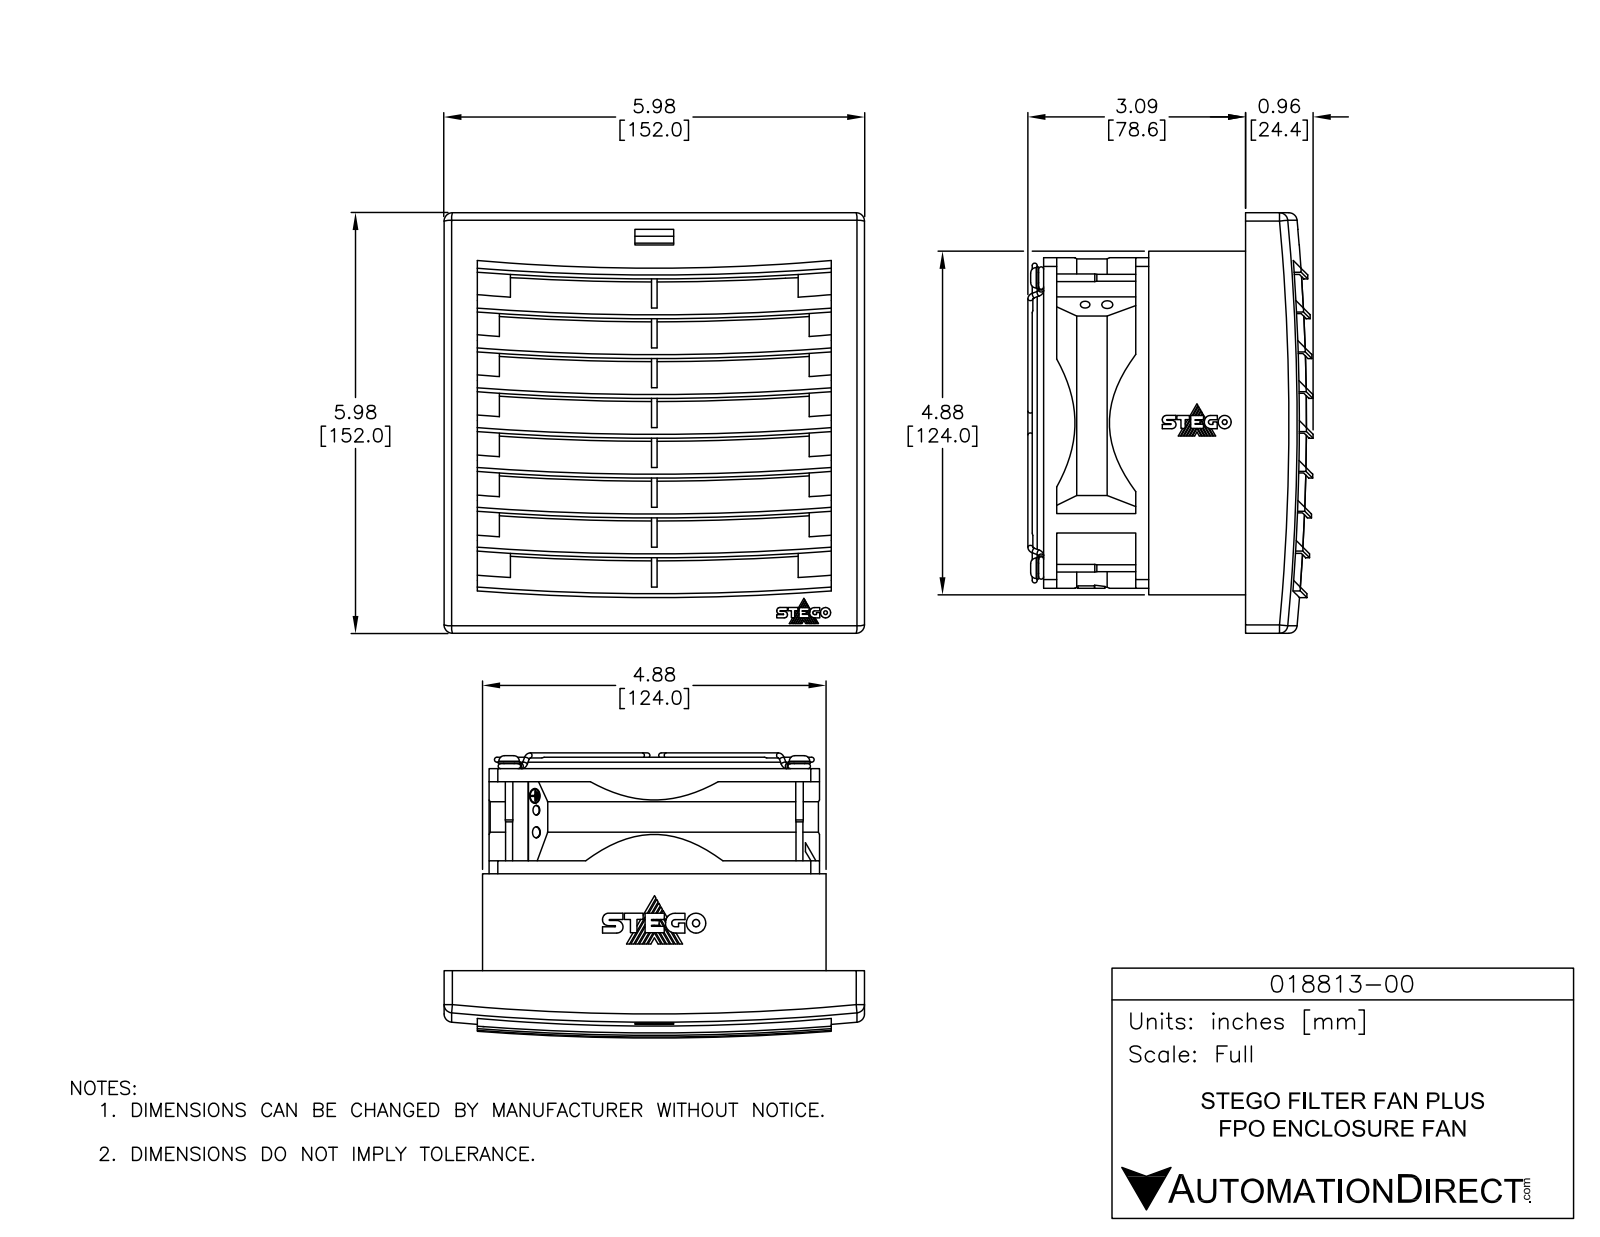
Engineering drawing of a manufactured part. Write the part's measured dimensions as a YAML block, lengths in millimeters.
part_name: "018813-00"
step_written_by: "SolidWorks 2018 (AUTOMOTIVE_DESIGN)"
units: millimeters
bodies: {solids: 1, faces: 544, planar: 329, cylindrical: 207, other: 8}
overall_size: [152, 152, 104]
volume: 537000
surface_area: 231900
round_holes:
  - {diameter: 6.5, count: 4}
  - {diameter: 24.9, count: 1}
  - {diameter: 42.2, count: 1}
  - {diameter: 59.4, count: 1}
  - {diameter: 76.7, count: 1}
  - {diameter: 82.6, count: 1}
  - {diameter: 96, count: 1}
  - {diameter: 105.4, count: 1}
round_bosses_or_shafts:
  - {diameter: 110.4, count: 1}
  - {diameter: 88.6, count: 1}
  - {diameter: 80.7, count: 1}
  - {diameter: 68.9, count: 1}
  - {diameter: 63.4, count: 1}
  - {diameter: 46.2, count: 1}
  - {diameter: 33.6, count: 1}
  - {diameter: 28.9, count: 1}
partial_cylinders:
  - {radius: 349.4, count: 16}
  - {radius: 47, count: 5}
  - {radius: 3, count: 4}
  - {radius: 3.6, count: 4}
  - {radius: 13.2, count: 1}
  - {radius: 21.6, count: 1}
  - {radius: 24.6, count: 1}
  - {radius: 31.4, count: 1}
face_to_face_distances: [1.5, 10.8, 3.1, 120.9, 21.6, 2, 3.4, 6.8, 12.3, 9.3]
hole_center_spacings: [76.4, 108, 152.7]
